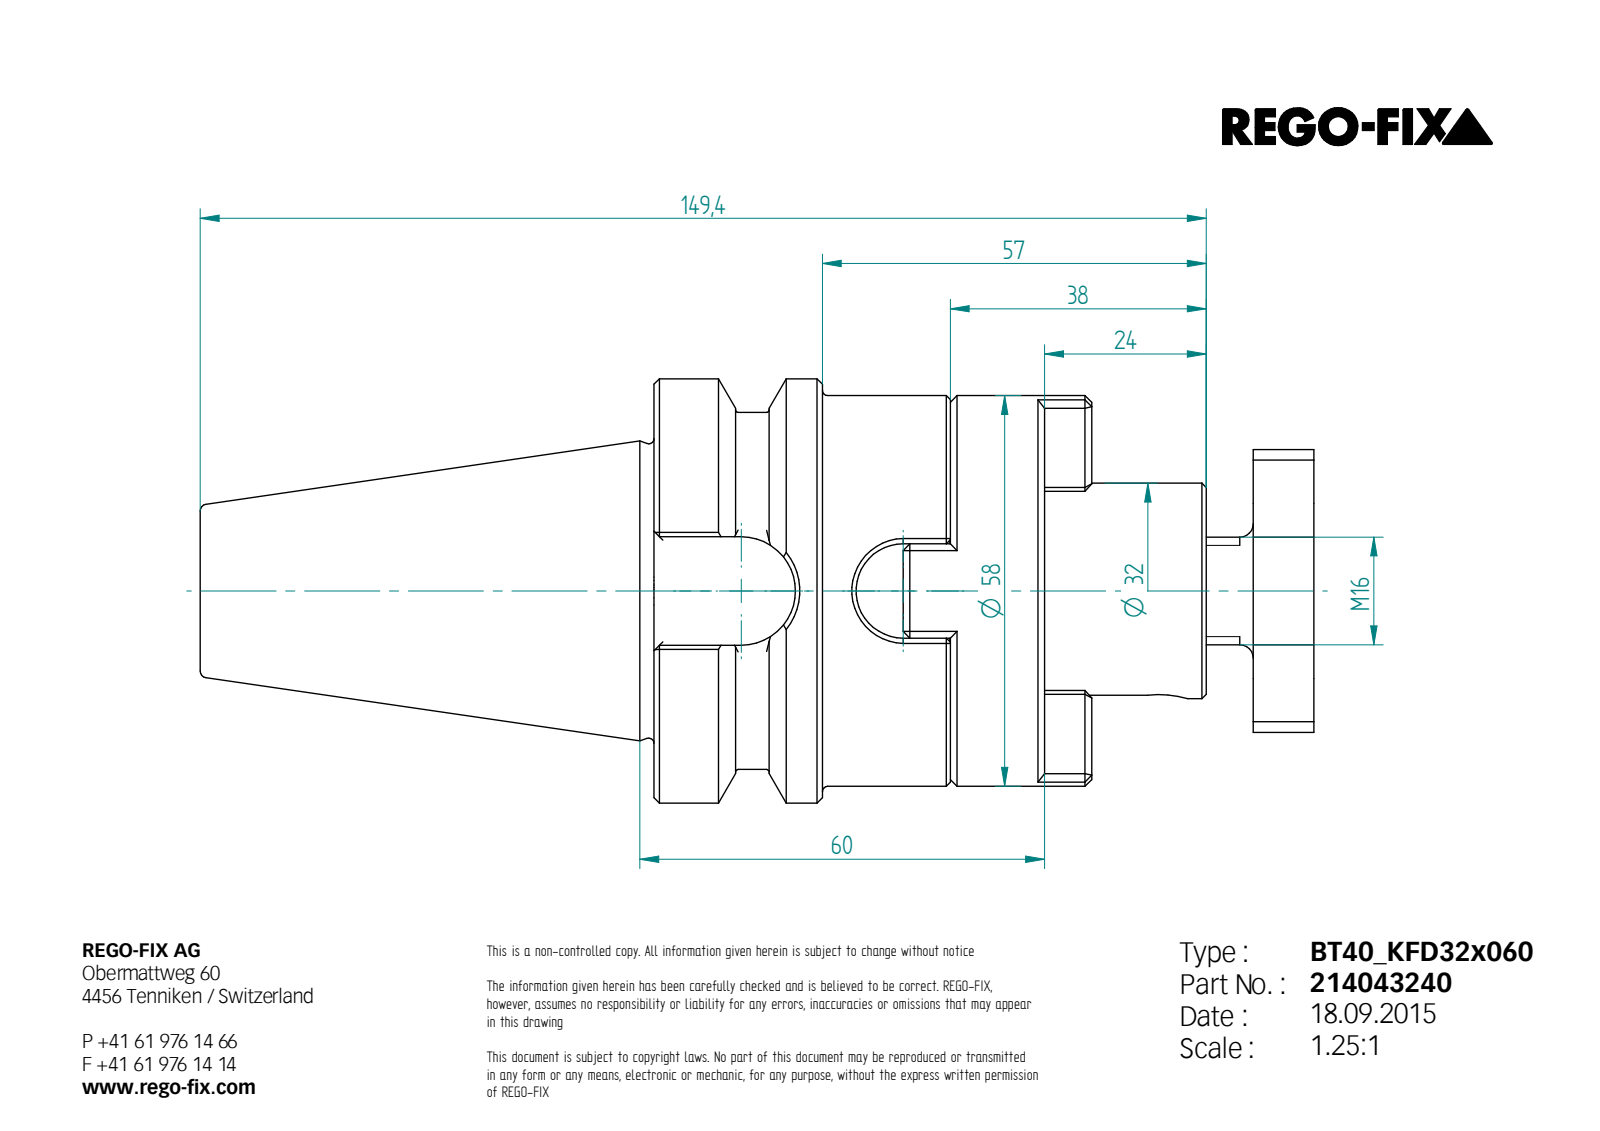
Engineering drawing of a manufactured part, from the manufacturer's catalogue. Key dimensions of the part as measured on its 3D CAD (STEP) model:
STEP written by: Unknown (AUTOMOTIVE_DESIGN)
Units: millimetres
Bodies: 3 solids, 213 faces (126 planar, 34 cylindrical, 53 other)
Overall size (bounding box): 165.4 × 63 × 63
Volume: 231 465 mm³ · Surface area: 46 059 mm²
Round holes (diameter × count): ⌀13.84 ×1, ⌀17 ×1, ⌀32 ×1
Round bosses / shafts (diameter × count): ⌀63 ×1, ⌀58 ×1, ⌀53 ×1, ⌀31.4 ×1, ⌀16 ×1
Partial cylindrical surfaces — rounded edges, fillets, slot ends (radius × count): R0.5 ×4, R5 ×4, R4 ×2, R7 ×1, R8.05 ×1, R21 ×1
Main face-to-face distances: 14, 40, 44, 58, 98, 54, 45, 7, 9, 89
